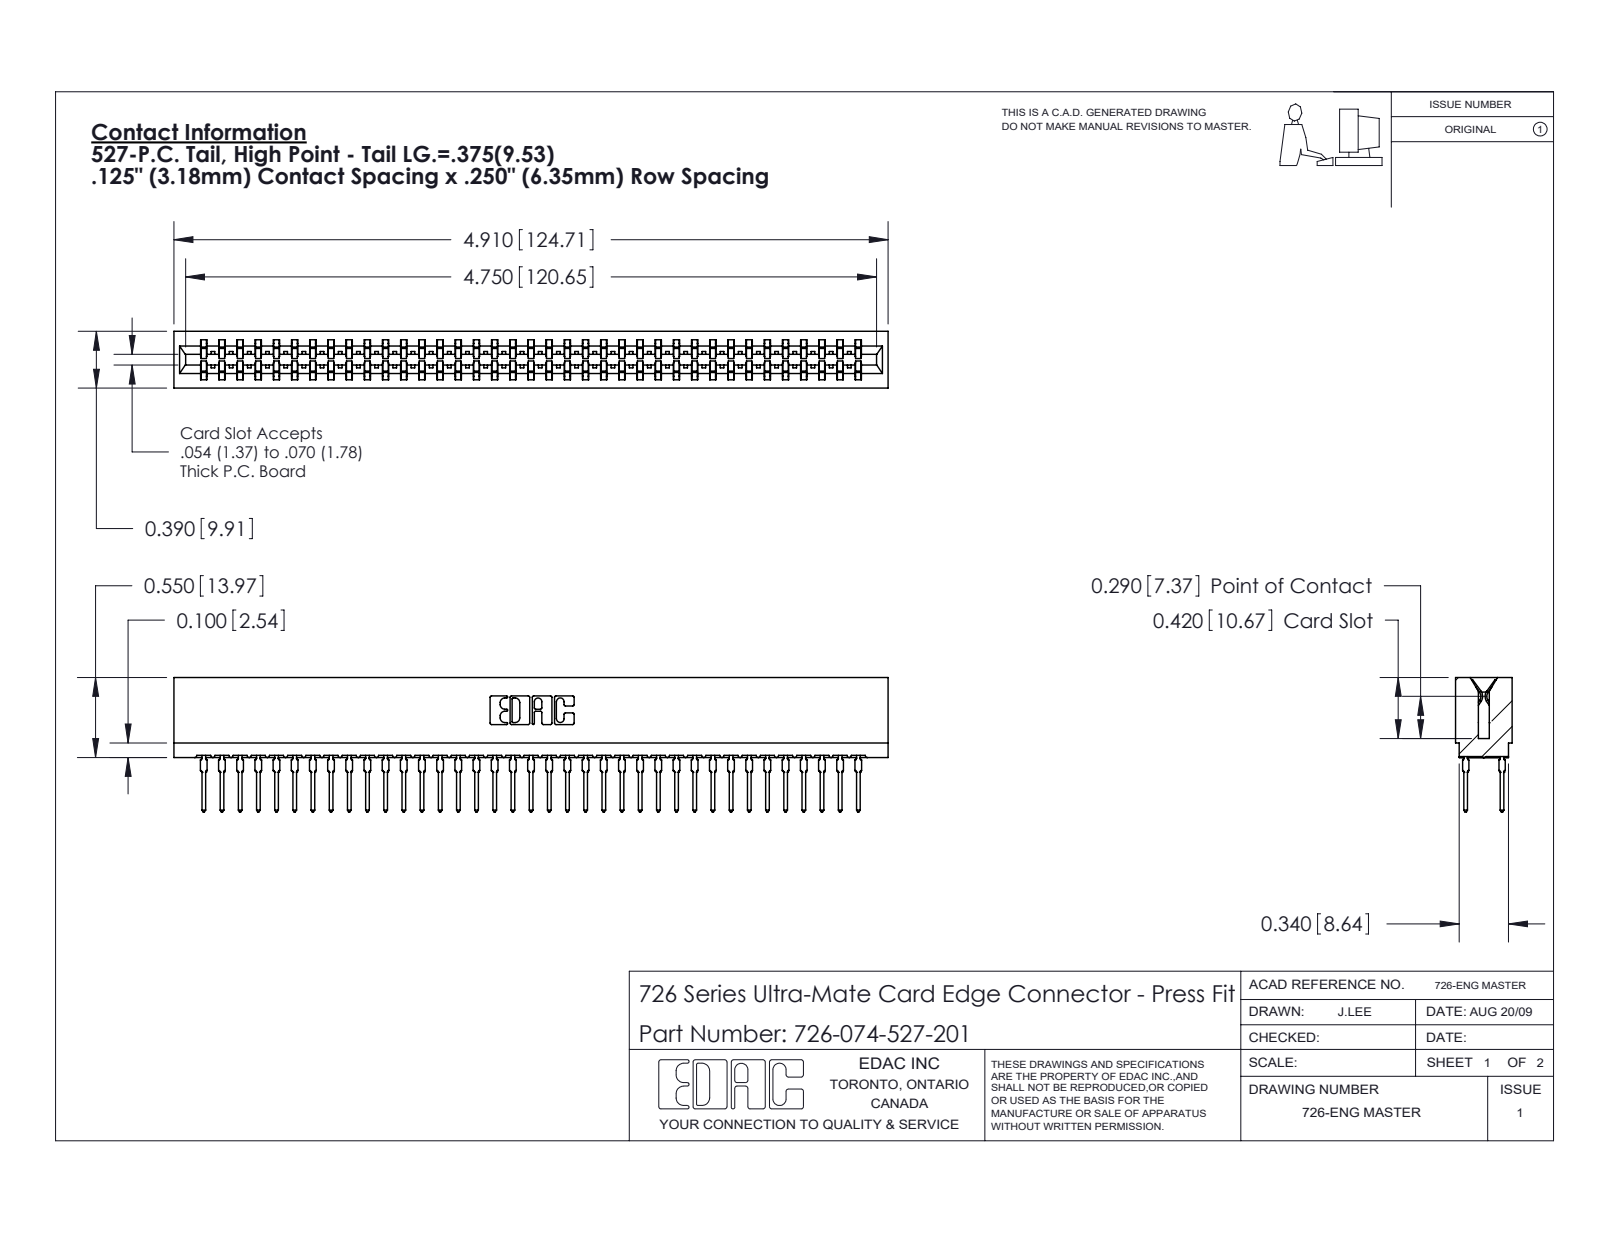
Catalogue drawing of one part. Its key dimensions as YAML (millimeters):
part_name: "746-292-001_527; 726-074-527-201; 726 Part_.515 Slot Depth - 01"
step_written_by: "SolidWorks 2020 (CONFIG_CONTROL_DESIGN)"
units: millimeters
bodies: {solids: 75, faces: 6720, planar: 3459, cylindrical: 1337, other: 1924}
overall_size: [124.7, 23.5, 9.9]
volume: 11600
surface_area: 19870
partial_cylinders:
  - {radius: 0.5, count: 148}
  - {radius: 0.4, count: 38}
  - {radius: 0.3, count: 22}
  - {radius: 0.1, count: 8}
  - {radius: 0.3, count: 8}
  - {radius: 0.2, count: 6}
  - {radius: 0.8, count: 6}
  - {radius: 0.7, count: 3}
face_to_face_distances: [1.4, 8.5, 6.4, 0.6, 7.8, 9.9, 7, 2.1, 12.7, 9.3]
